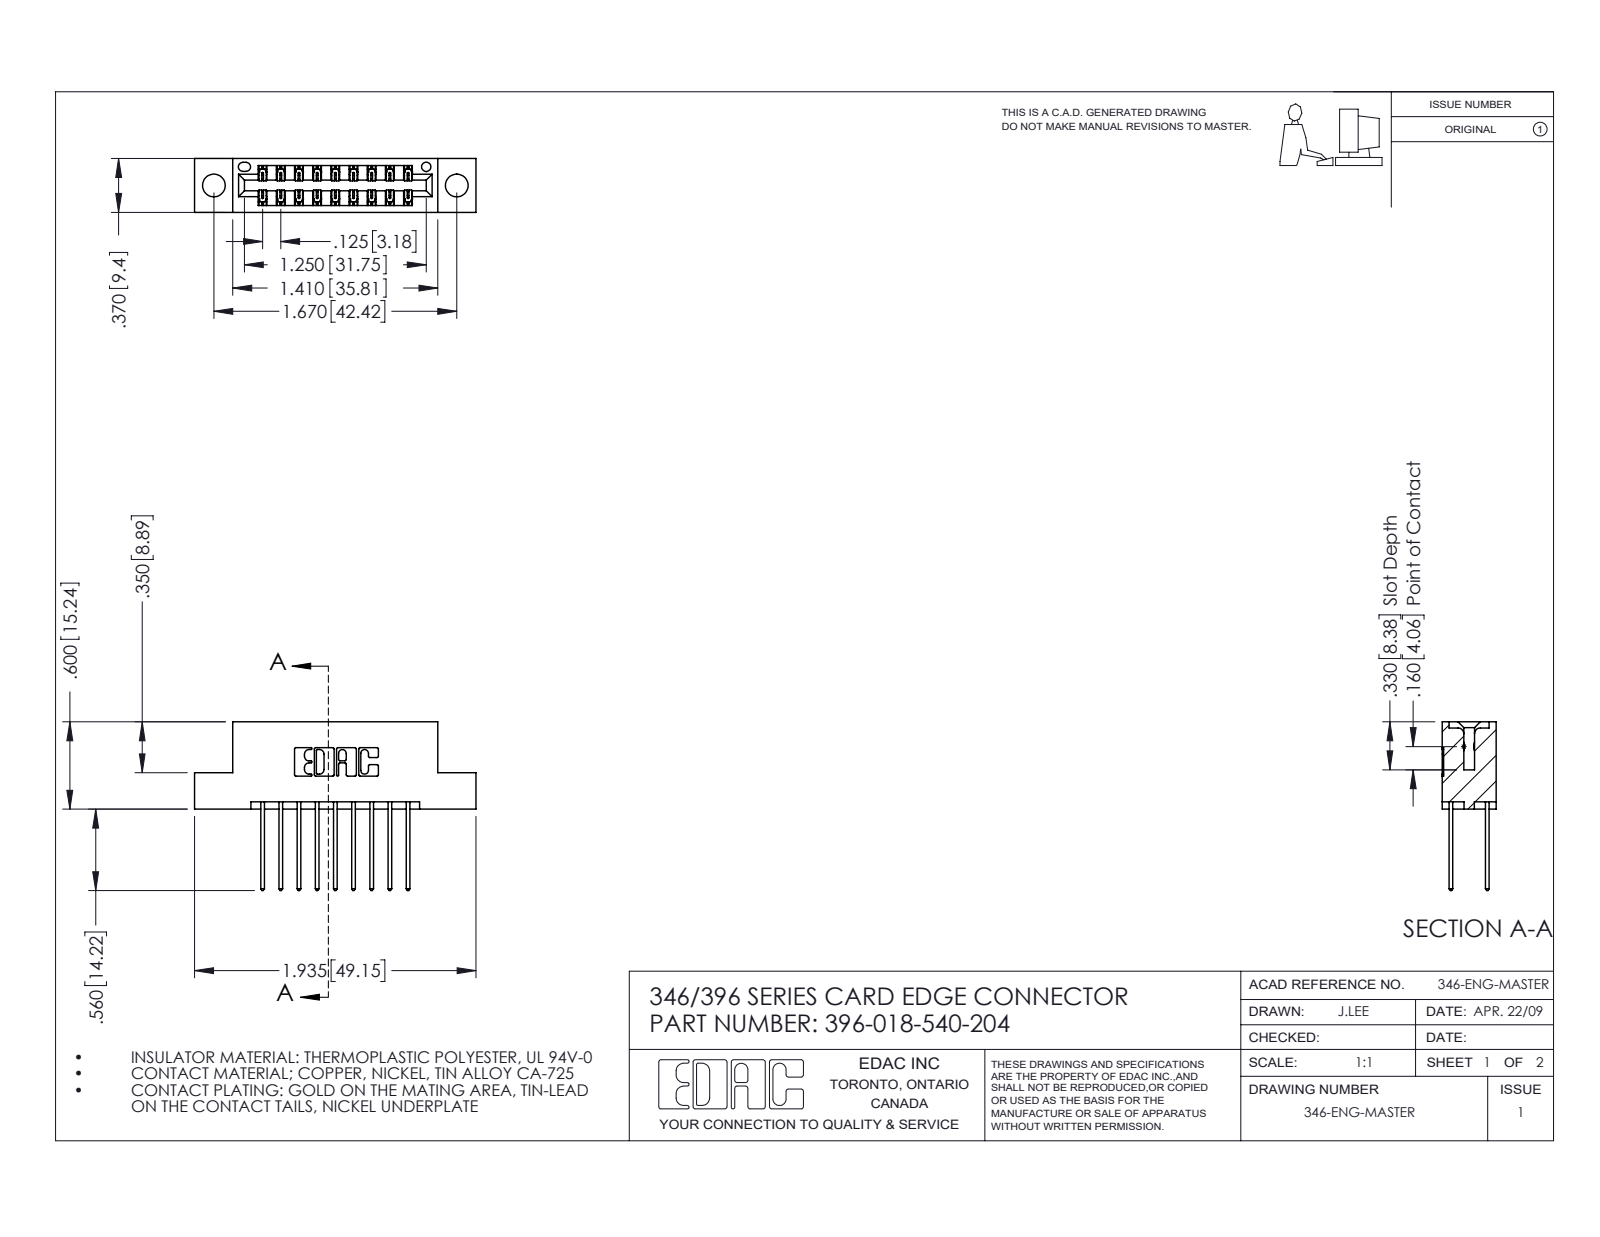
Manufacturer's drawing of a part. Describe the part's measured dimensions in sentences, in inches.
The part is named "346 Part_Flush Mounting Lugs - 0.156 Dia-TH; 396-018-540-204; 345-292-001_345-293-140". Its 3-D file was written by "SolidWorks 2016 (CONFIG_CONTROL_DESIGN)". It is 19 solids with 1058 faces: 706 planar, 352 cylindrical and 0 other. Overall it measures 1.935 by 1.16 by 0.37 inches. Its volume is 0.276 cubic inches and its surface area 9.03 square inches. Round holes: 2 of diameter 0.156, 1 of diameter 0.064. Partial cylindrical surfaces (rounded edges, fillets, slot ends): 27 of radius 0.006, 22 of radius 0.01, 18 of radius 0.01, 6 of radius 0.007, 6 of radius 0.031, 3 of radius 0.026, 2 of radius 0.014, 2 of radius 0.022. The main face-to-face distances are 0.25, 0.048, 0.322, 0.37, 0.072, 0.298, 0.025, 0.275, 0.148, 0.222. The hole center spacings are 0.246, 1.465, 1.67.
